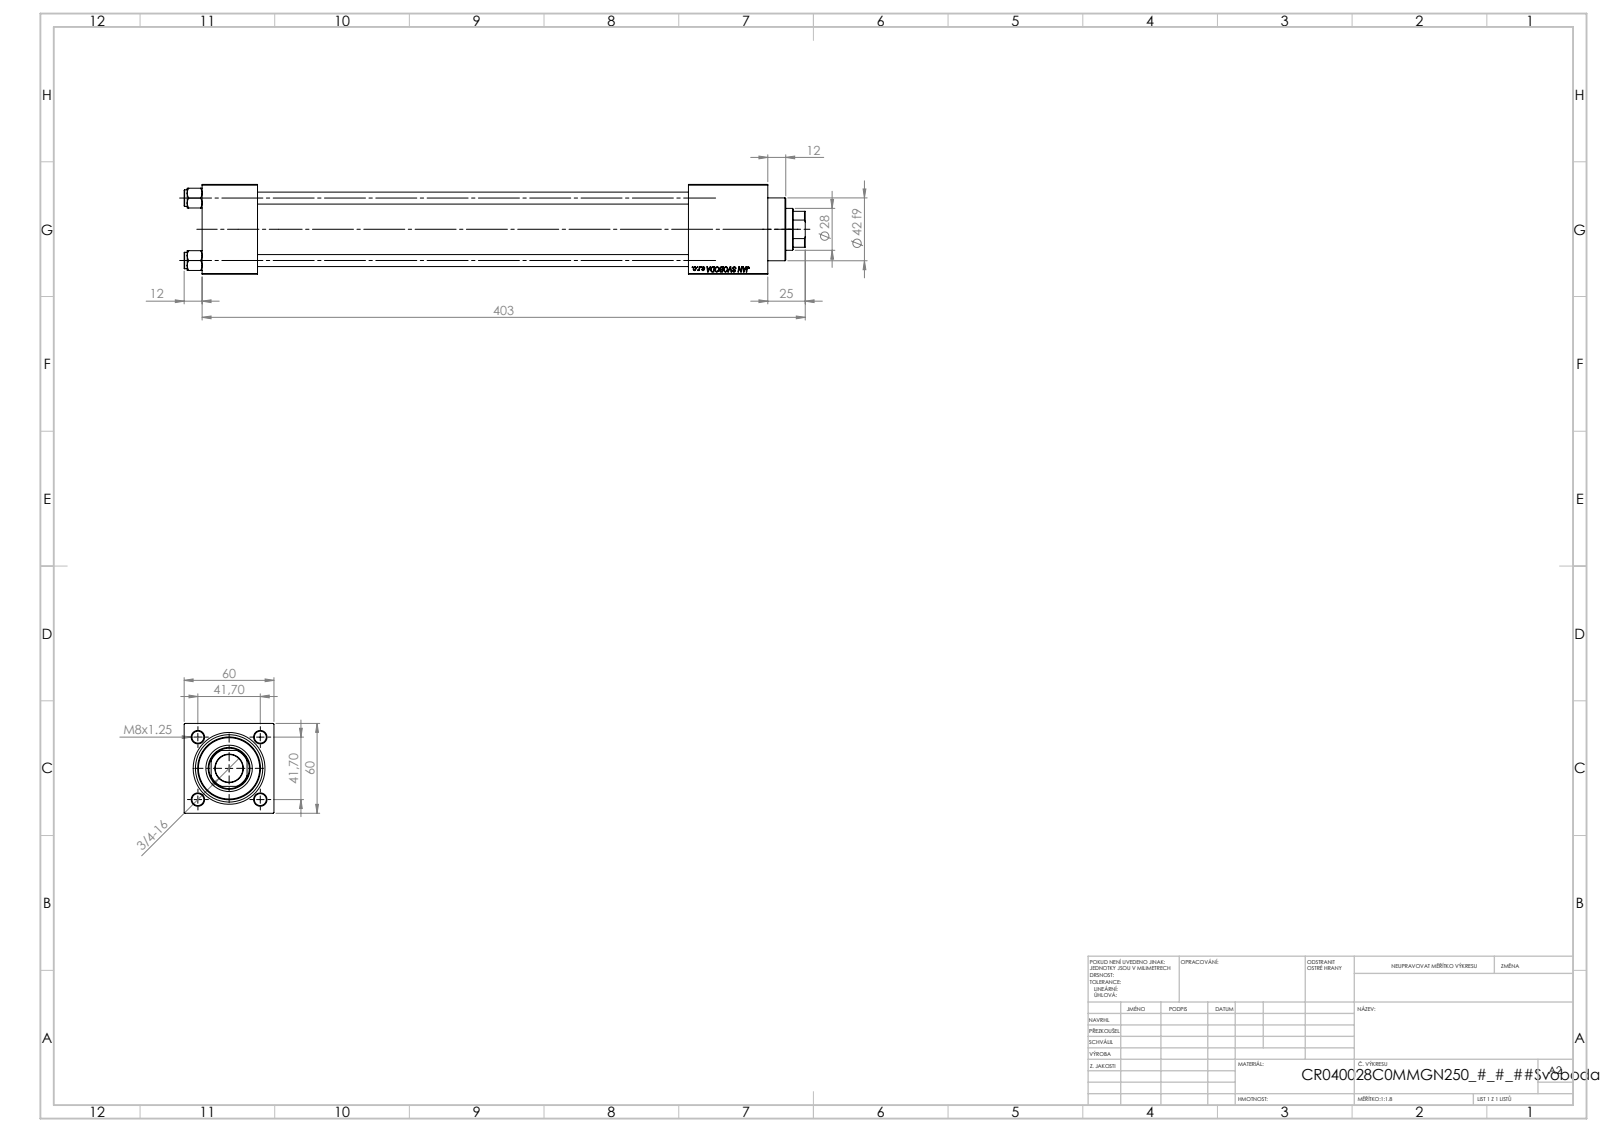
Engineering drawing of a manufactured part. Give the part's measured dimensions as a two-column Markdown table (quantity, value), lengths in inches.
| quantity | value |
| --- | --- |
| part name | V215CR_VCP_C; NUT_M5_C; V215CR_C_TYCINKA; V215CR_C_Body (+1 more) |
| STEP written by | SolidWorks 2019 (CONFIG_CONTROL_DESIGN) |
| units | inches |
| bodies | 11 solids, 1148 faces (526 planar, 86 cylindrical, 536 other) |
| overall size | 16.339 × 2.362 × 2.362 |
| volume | 43.06 in³ |
| surface area | 336.1 in² |
| round holes (diameter × count) | 0.315 × 4, 0.276 × 2, 0.656 × 2, 0.945 × 2, 0.728 × 1, 1.102 × 1, 1.22 × 1, 1.575 × 1, 1.772 × 1 |
| round bosses / shafts (diameter × count) | 0.433 × 4, 1.811 × 1, 1.654 × 1 |
| partial cylindrical surfaces (radius × count) | 0.531 × 1 |
| main face-to-face distances | 2.362, 1.457, 12.795, 11.339, 13.752, 12.295, 0.957, 2.087, 14.882, 13.425 |
| hole center spacings | 1.161, 1.642, 2.322, 12.697 |
